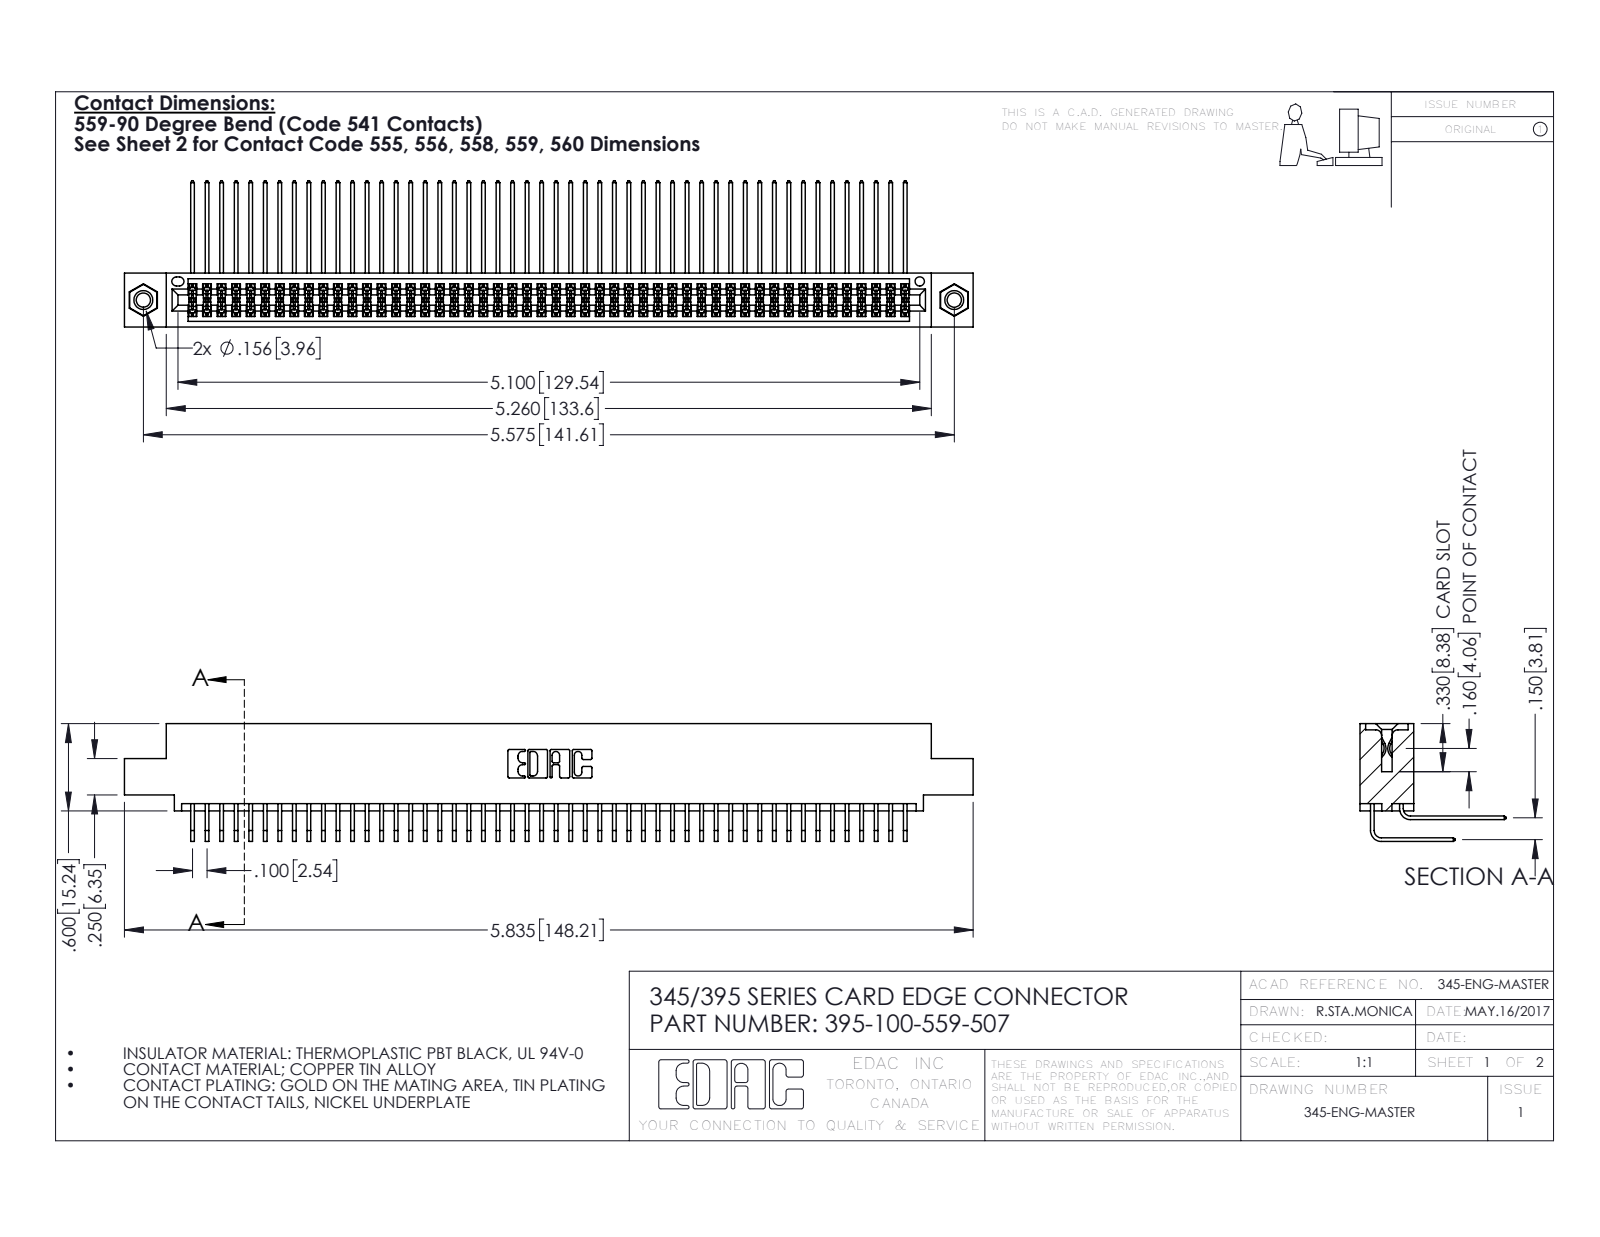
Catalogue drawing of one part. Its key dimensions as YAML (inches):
part_name: "345-292-001_559 Tail - 2; 345 Part_0.110 Offset - 0.156 Dia-TI; 345-250-001_345-250-005-103; 395-100-559-507 (+1 more)"
step_written_by: "SolidWorks 2016 (CONFIG_CONTROL_DESIGN)"
units: inches
bodies: {solids: 103, faces: 5390, planar: 3616, cylindrical: 1758, other: 16}
overall_size: [5.835, 1.005, 0.809]
volume: 0.913
surface_area: 38.91
round_holes:
  - {diameter: 0.098, count: 2}
  - {diameter: 0.125, count: 2}
  - {diameter: 0.156, count: 2}
  - {diameter: 0.064, count: 1}
round_bosses_or_shafts:
  - {diameter: 0.155, count: 2}
partial_cylinders:
  - {radius: 0.006, count: 151}
  - {radius: 0.01, count: 22}
  - {radius: 0.007, count: 6}
  - {radius: 0.031, count: 6}
  - {radius: 0.026, count: 3}
  - {radius: 0.014, count: 2}
  - {radius: 0.019, count: 2}
  - {radius: 0.022, count: 2}
face_to_face_distances: [0.072, 0.298, 0.2, 0.37, 0.098, 0.272, 0.025, 0.225, 0.175, 0.15]
hole_center_spacings: [0.27, 5.339, 5.575]
